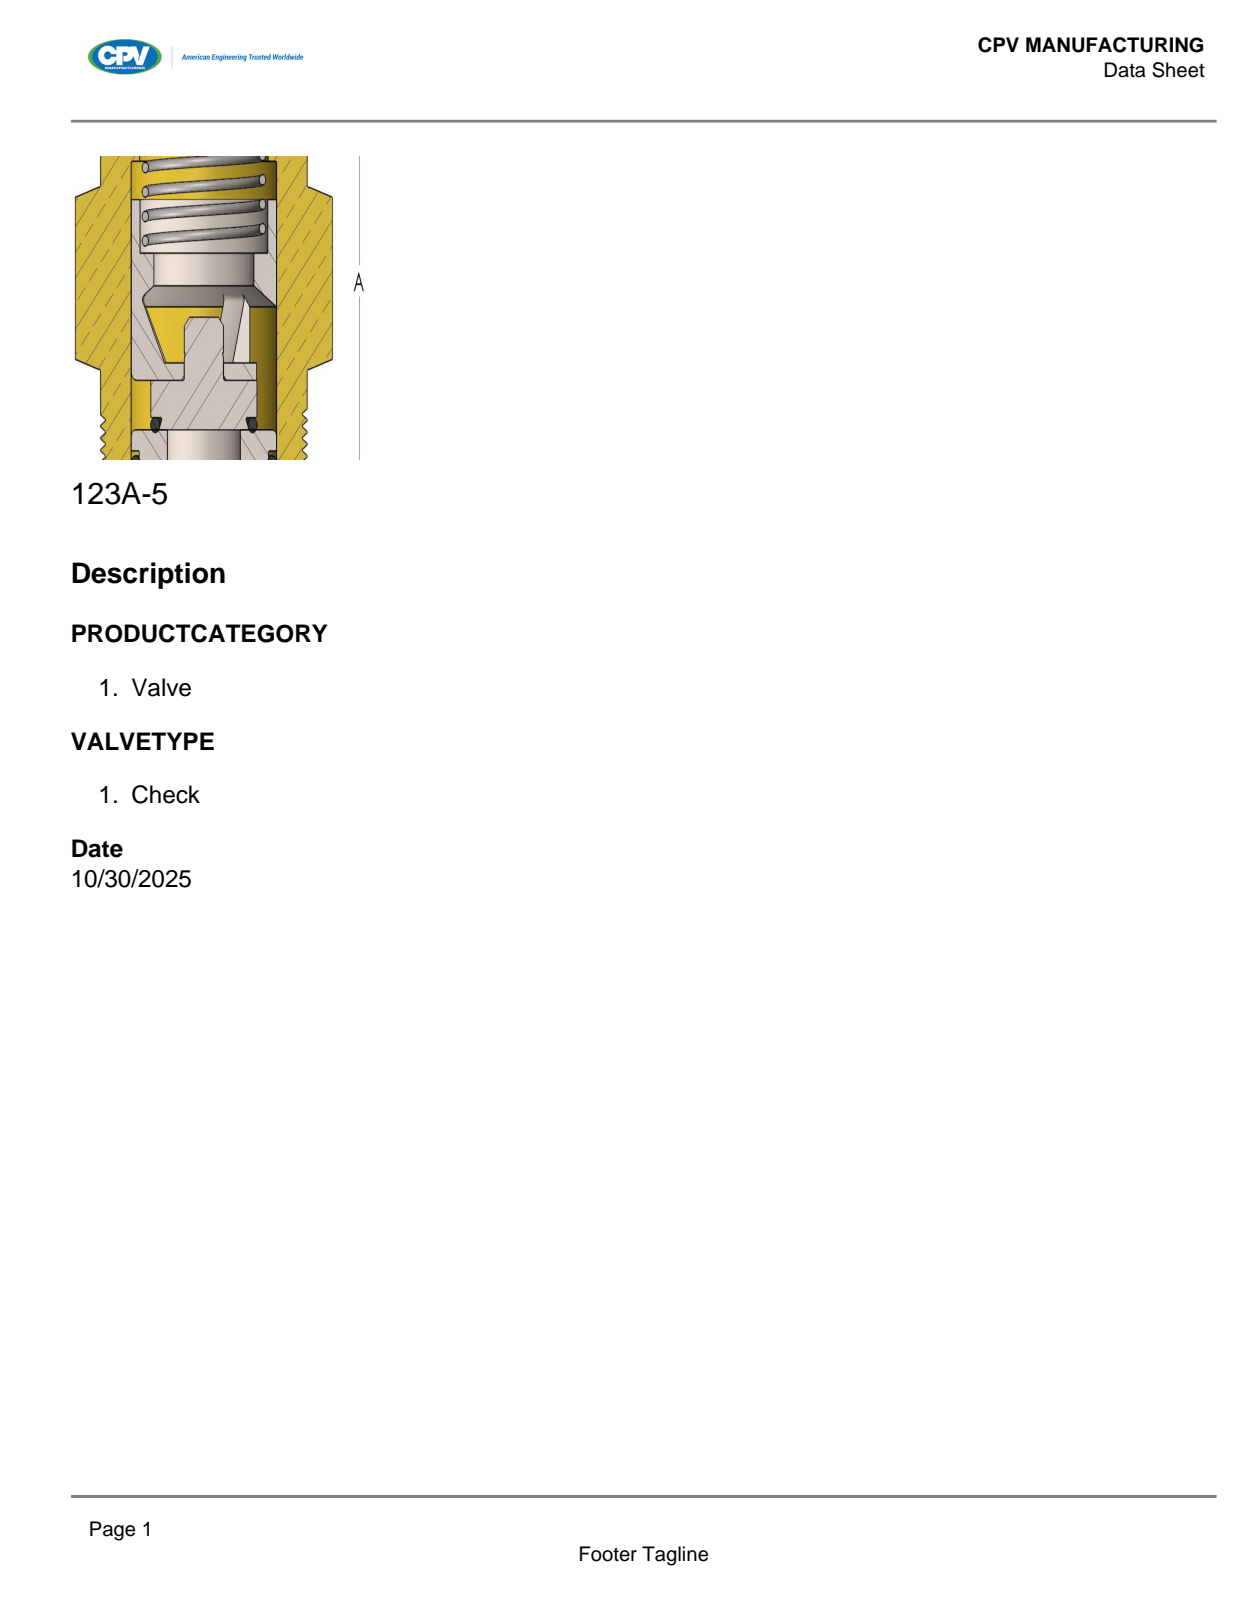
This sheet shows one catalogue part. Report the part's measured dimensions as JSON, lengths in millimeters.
{"part_name": "123A-5", "step_written_by": "SolidWorks 2018 (AUTOMOTIVE_DESIGN)", "units": "millimeters", "bodies": {"solids": 1, "faces": 67, "planar": 11, "cylindrical": 38, "other": 18}, "overall_size": [73.5, 69.9, 63.5], "volume_mm3": 220900, "surface_area_mm2": 26320, "round_holes": [[20.6, 1], [20.8, 1]], "round_bosses_or_shafts": [[58.6, 1], [45.8, 1]], "partial_cylinders_radius": [[34.9, 1]], "face_to_face_distances": [73.5, 53, 20.6, 21, 32, 52.6, 63.5, 0.4, 20.6, 52.6]}
